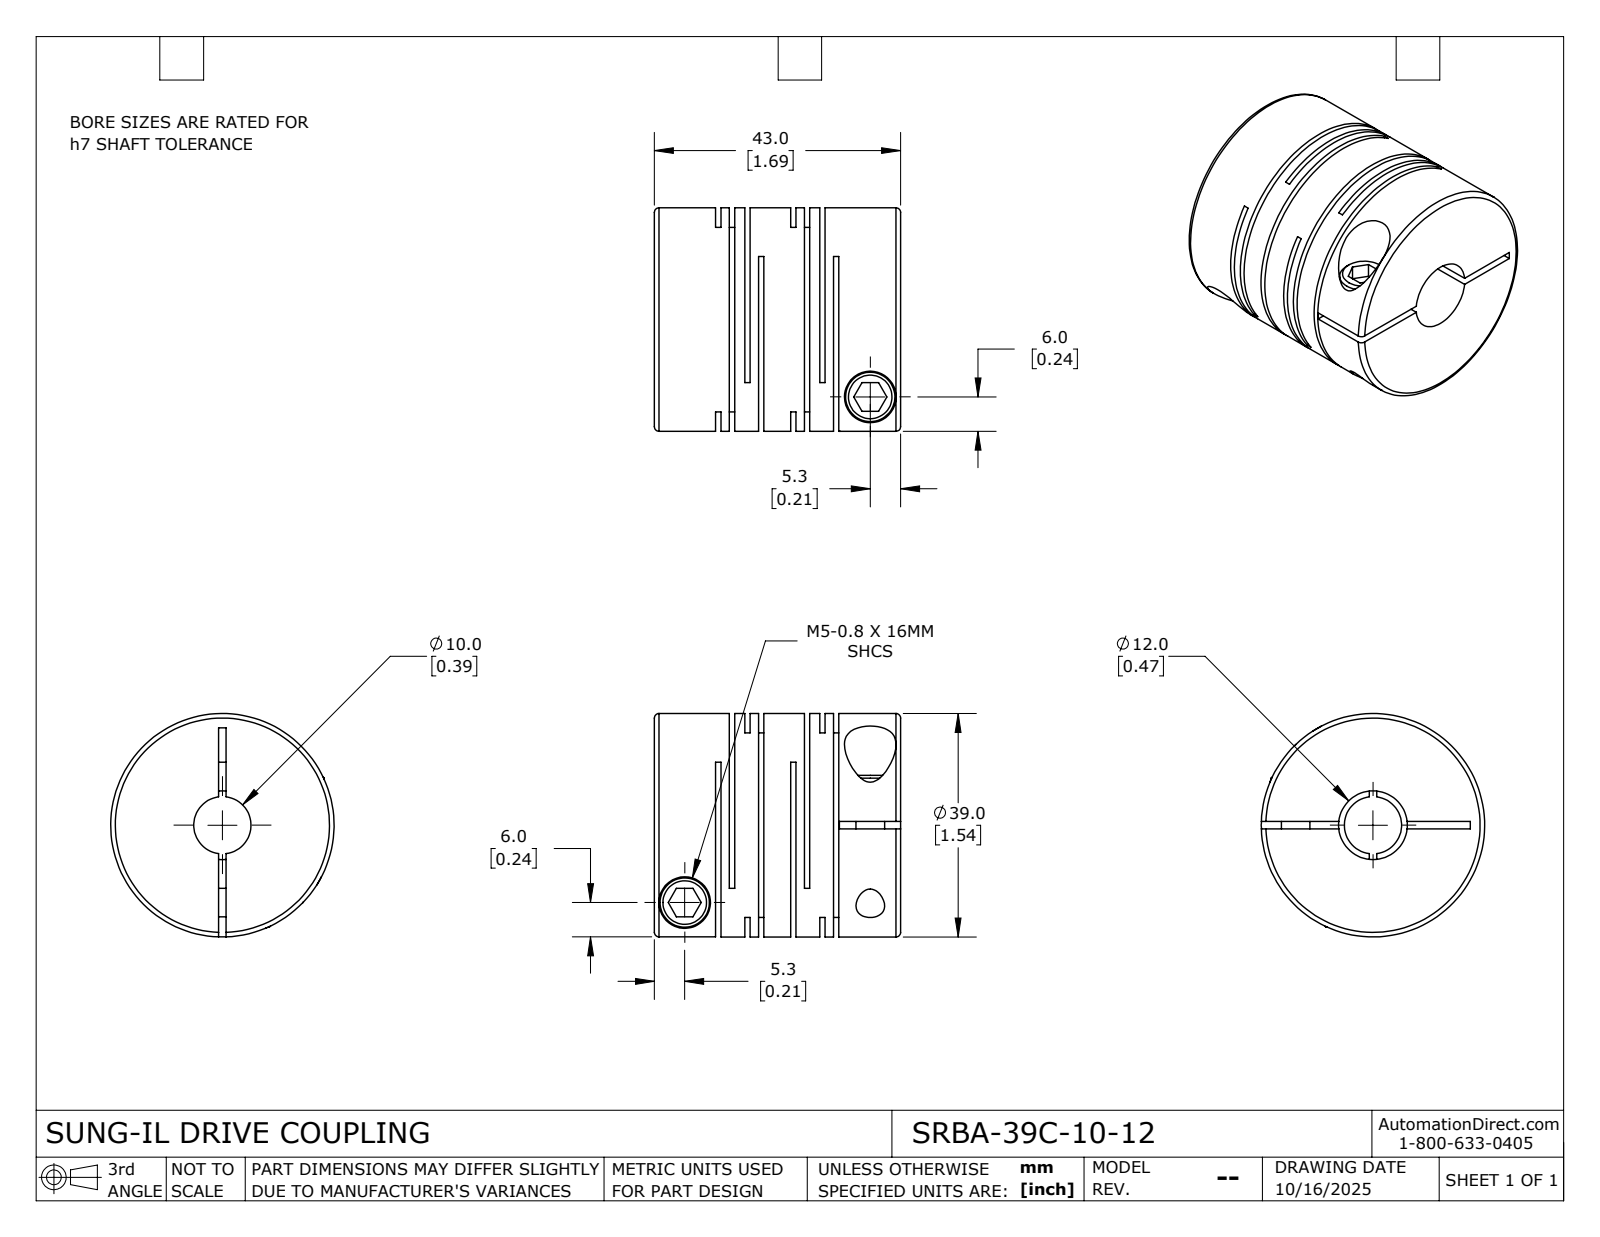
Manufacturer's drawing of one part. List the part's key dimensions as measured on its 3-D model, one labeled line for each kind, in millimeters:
Part name (STEP PRODUCT): SRBA-39C-10-12
STEP written by: SolidWorks 2024 (CONFIG_CONTROL_DESIGN)
Units: millimetres
Bodies: 1 solid, 115 faces (60 planar, 42 cylindrical, 13 other)
Overall size (bounding box): 43 × 39 × 39
Volume: 38 728 mm³ · Surface area: 24 283 mm²
Round holes (diameter × count): ⌀5 ×2, ⌀9 ×2, ⌀10 ×1, ⌀12 ×1
Round bosses / shafts (diameter × count): ⌀8.6 ×2, ⌀39 ×1
Main face-to-face distances: 13.1, 0.92, 2.4, 5.1, 10.7, 14.02, 18.2, 12.18, 3.32, 15.5
